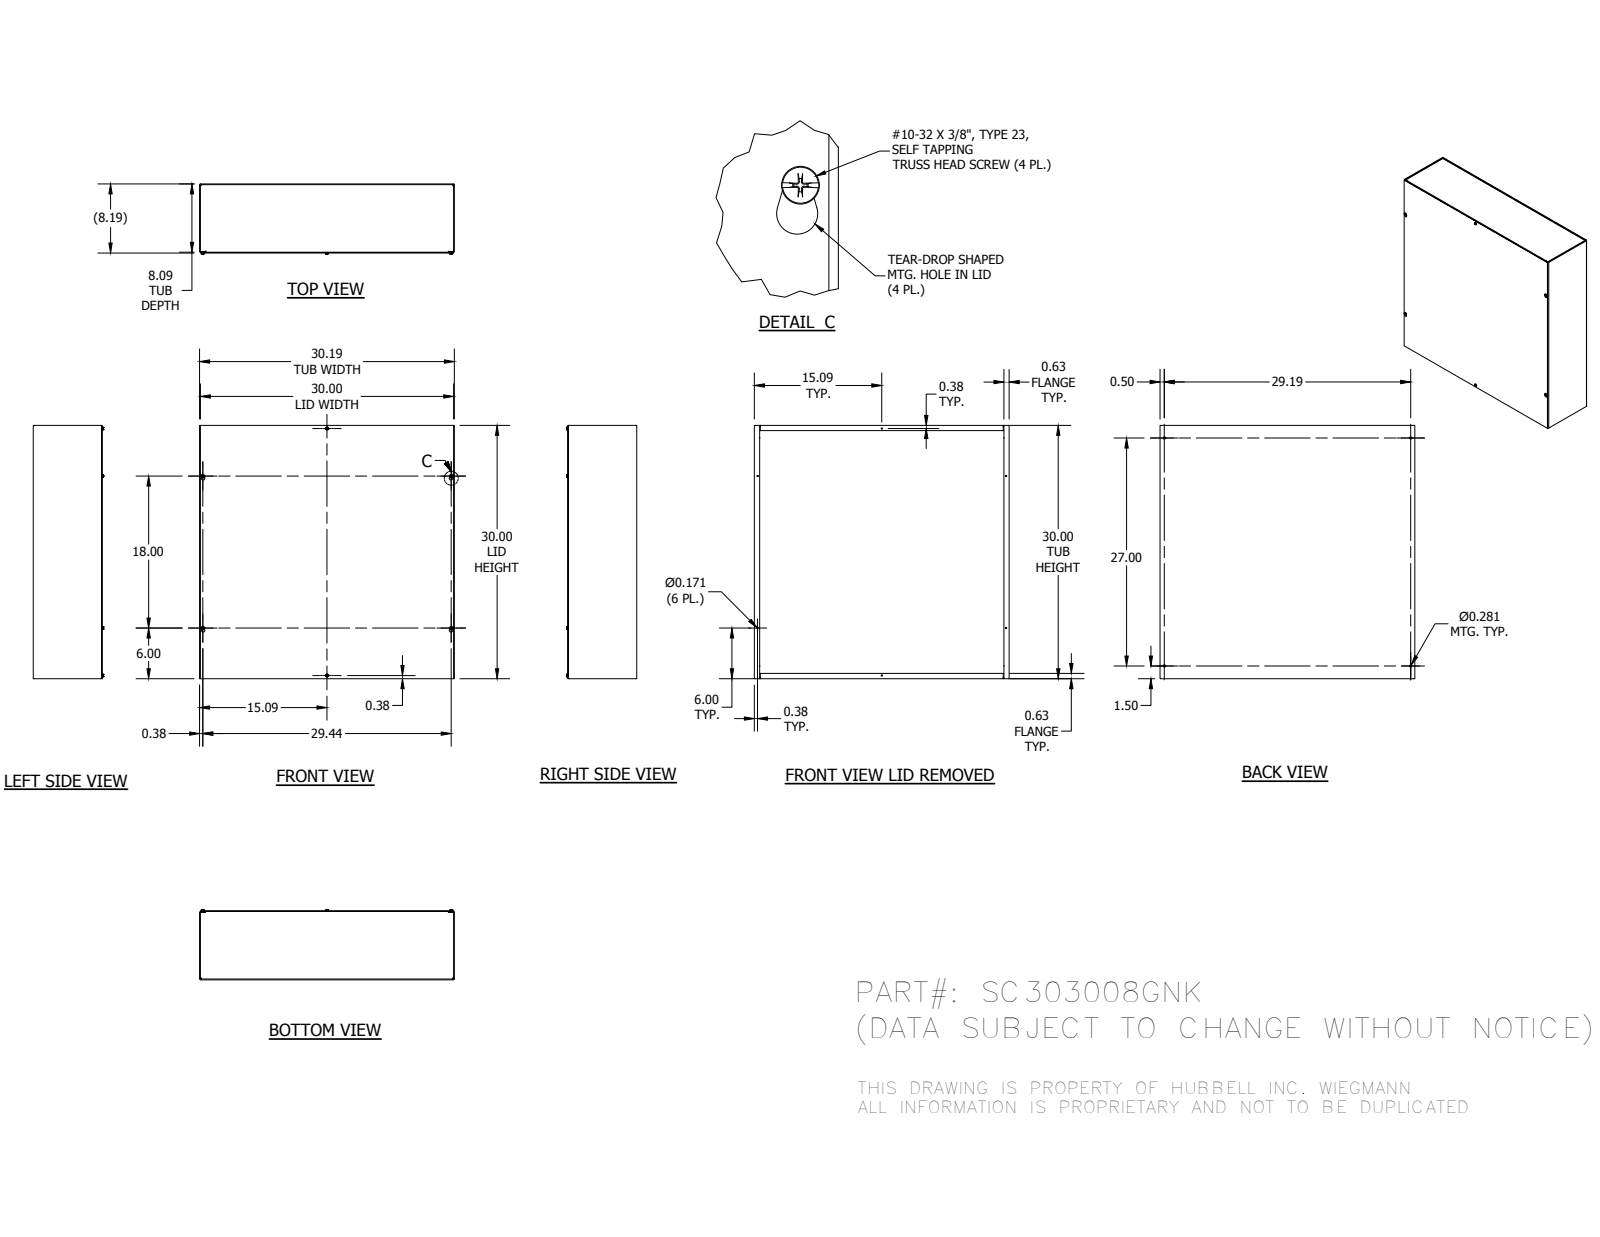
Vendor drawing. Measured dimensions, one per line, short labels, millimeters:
name: SC303008GNKBLR; SC3008GNKTB; SC3030GLPA; 37214 (+1 more)
written by: Autodesk Inventor 2014 (AUTOMOTIVE_DESIGN)
unit: mm
bodies: 10 solids, 404 faces (232 planar, 50 cylindrical, 122 other)
size: 766.76 × 762 × 211.31
volume: 4 407 000 mm³; area: 3 730 000 mm²
holes: 6× ⌀4.34, 4× ⌀7.14, 2× ⌀7.92
bosses: 6× ⌀4.83
rounds: 12× R0.4, 12× R2.78, 4× R3.17, 4× R5.16
face distances: 2.38, 205.58, 203.2, 207.96, 762, 759.62, 764.38, 757.24, 766.76, 4.76
hole spacings: 371.78, 400.23, 804.82, 114.34, 571.51, 707, 753.26, 938.59
